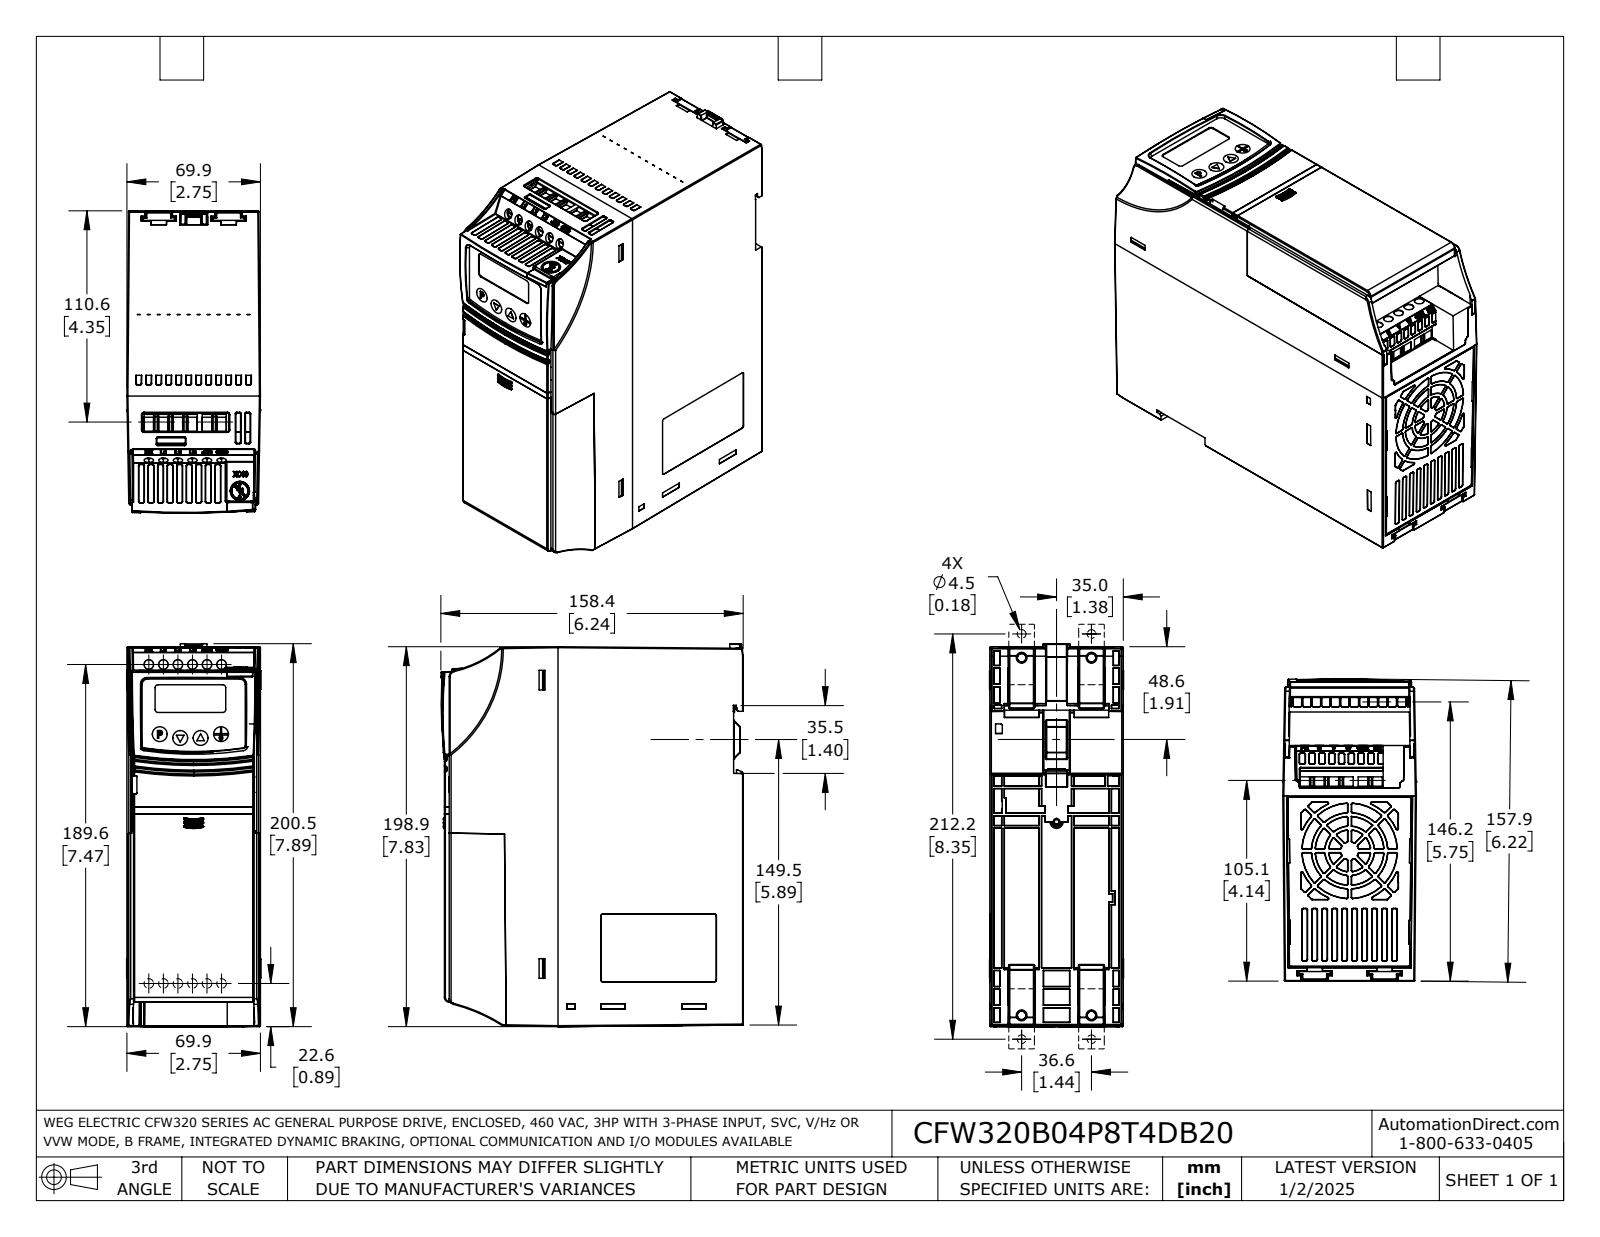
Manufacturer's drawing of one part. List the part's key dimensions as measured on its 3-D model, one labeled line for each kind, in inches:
Part name (STEP PRODUCT): CFW320B04P8T4DB20
STEP written by: SolidWorks 2021 (AUTOMOTIVE_DESIGN)
Units: inches
Bodies: 5 solids, 3984 faces (1907 planar, 899 cylindrical, 1178 other)
Overall size (bounding box): 7.894 × 6.235 × 2.764
Volume: 24.51 in³ · Surface area: 385.1 in²
Round holes (diameter × count): ⌀0.193 ×6
Partial cylindrical surfaces — rounded edges, fillets, slot ends (radius × count): R0.012 ×355, R0.02 ×181, R0.039 ×14, R0.03 ×7, R0.118 ×5, R0.01 ×2, R0.109 ×2, R0.098 ×1
Main face-to-face distances: 0.209, 0.098, 0.1, 5.826, 5.728, 0.211, 5.939, 6.037, 7.5, 0.039
Hole centre spacings: 0.3, 0.6, 0.9, 1.2, 1.5
